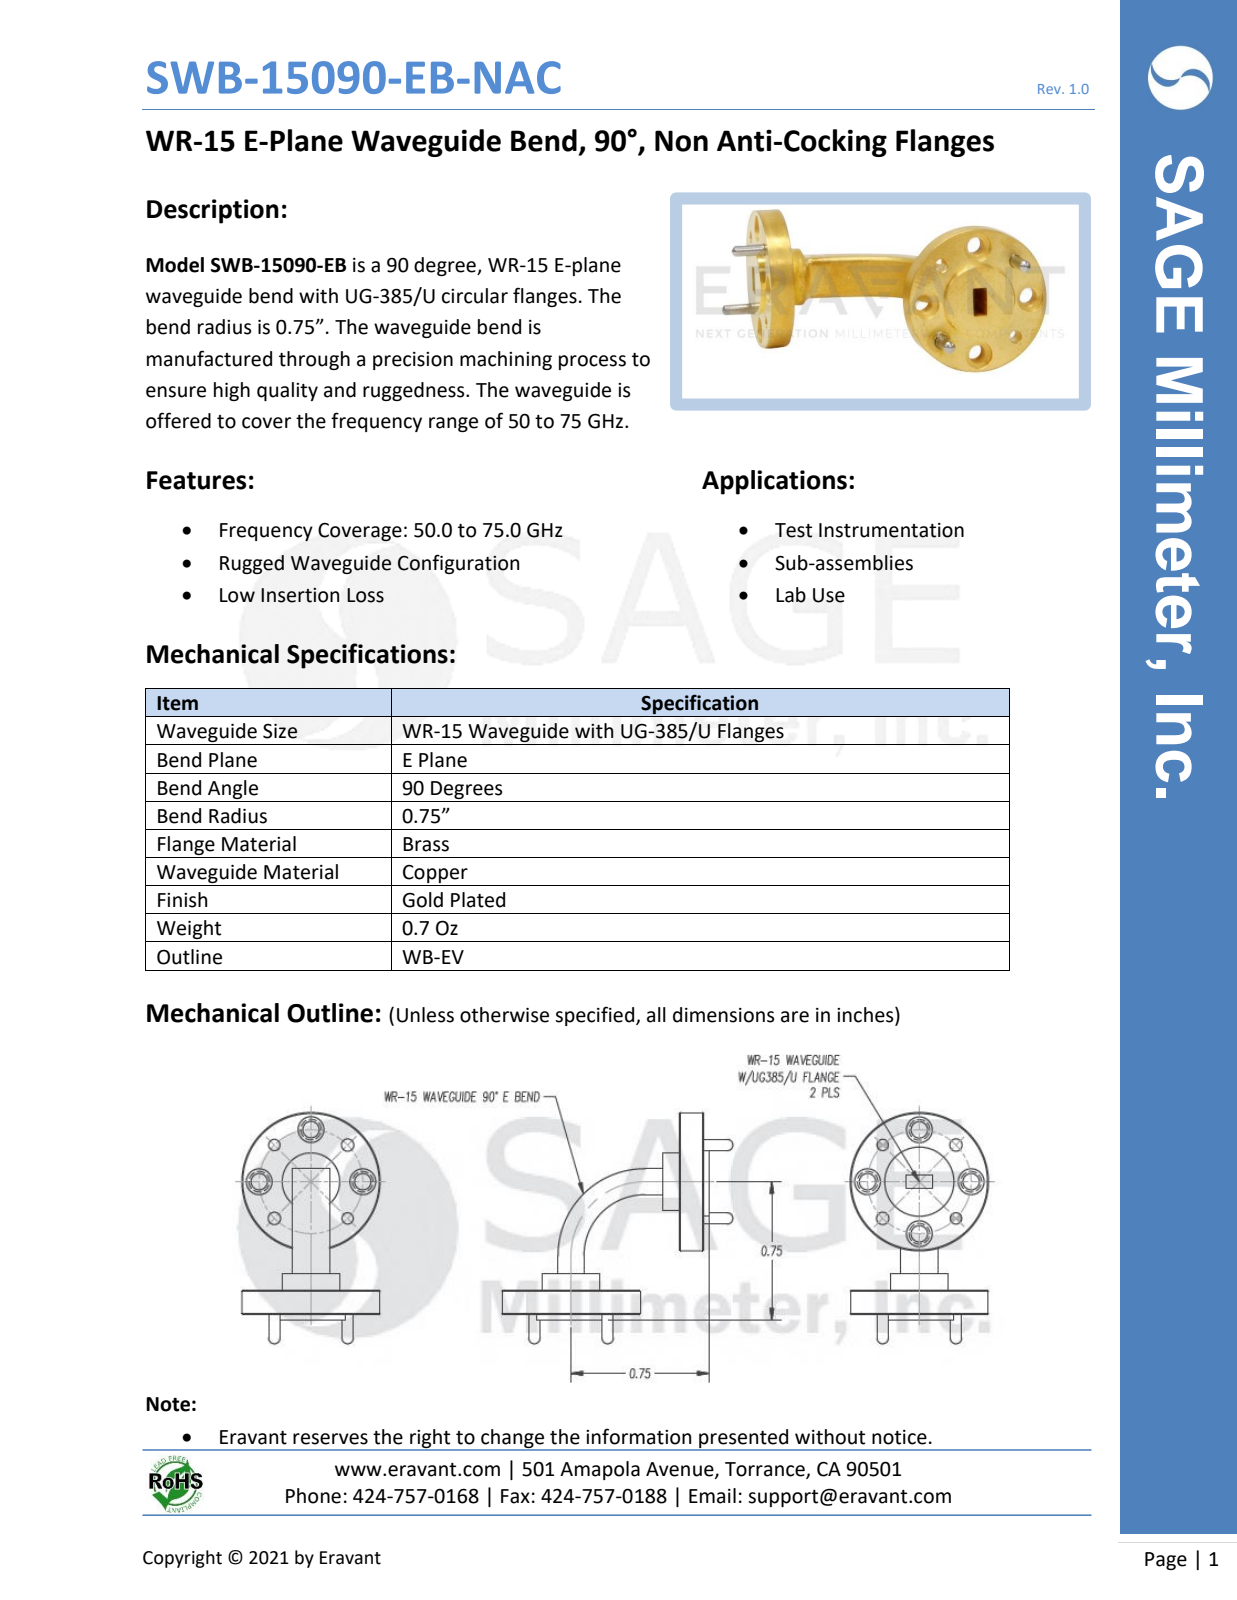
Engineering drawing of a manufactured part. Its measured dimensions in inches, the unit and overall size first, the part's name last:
Units: inches
Overall size (bounding box): 1.278 × 1.278 × 0.75
Round holes (diameter × count): ⌀0.089 ×8, ⌀0.14 ×8, ⌀0.059 ×4, ⌀0.067 ×4
Round bosses / shafts (diameter × count): ⌀0.063 ×4, ⌀0.75 ×2, ⌀0.375 ×2, ⌀0.35 ×2
Partial cylindrical surfaces — rounded edges, fillets, slot ends (radius × count): R0.373 ×1, R0.527 ×1
Main face-to-face distances: 0.13, 0.04, 0.03, 0.16, 0.188, 0.26, 0.23, 0.1, 0.228, 0.148
Hole centre spacings: 0.215, 0.398, 0.519, 0.562
Bodies: 0 solids, 146 faces (36 planar, 70 cylindrical, 40 other)
Part name (STEP PRODUCT): SWB-15090-EB
STEP written by: SolidWorks 2013 (CONFIG_CONTROL_DESIGN)
